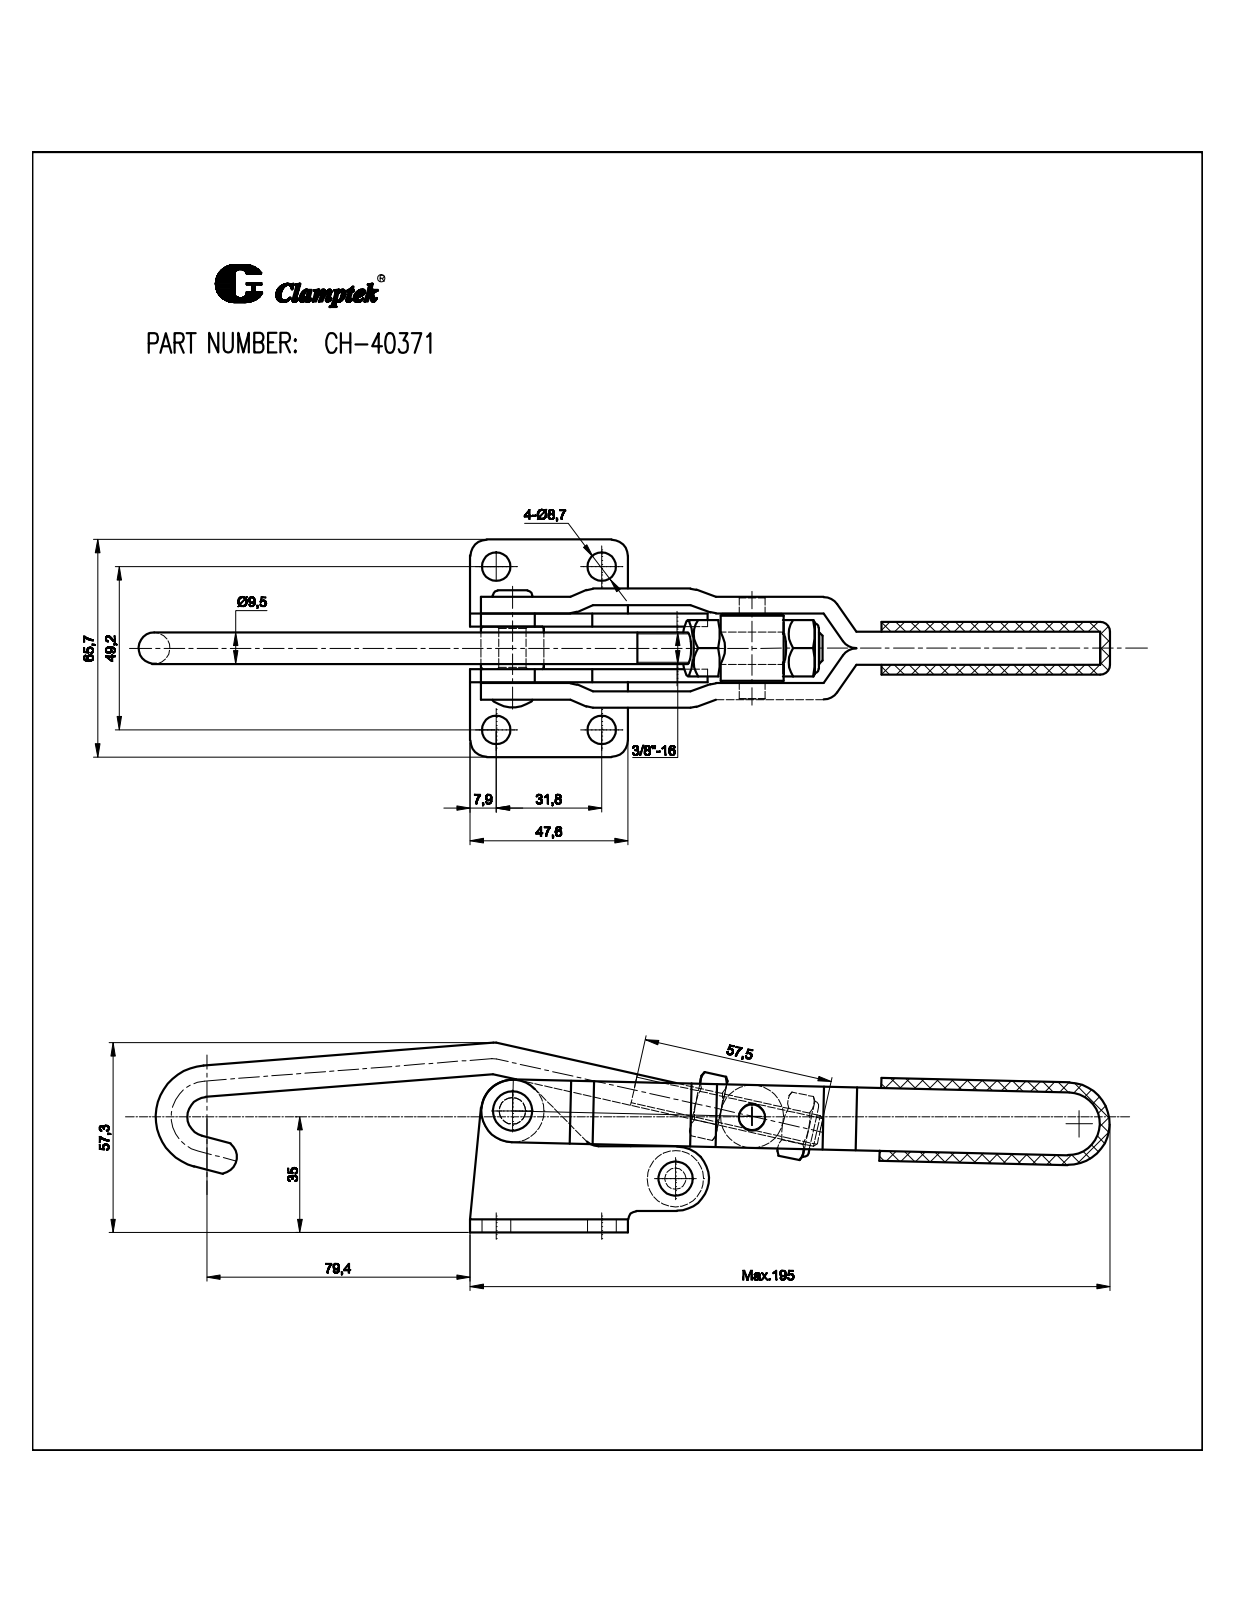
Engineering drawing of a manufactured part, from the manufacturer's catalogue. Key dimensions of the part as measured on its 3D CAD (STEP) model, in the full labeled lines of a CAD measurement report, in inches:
Part name (STEP PRODUCT): CH-40371
STEP written by: SolidWorks 2008 (CONFIG_CONTROL_DESIGN)
Units: inches
Bodies: 13 solids, 717 faces (243 planar, 235 cylindrical, 239 other)
Overall size (bounding box): 11.422 × 2.583 × 2.22
Volume: 5.747 in³ · Surface area: 92.11 in²
Round holes (diameter × count): ⌀0.343 ×4, ⌀0.335 ×3, ⌀0.315 ×2, ⌀0.06 ×1, ⌀0.181 ×1, ⌀0.236 ×1, ⌀0.252 ×1, ⌀0.256 ×1, ⌀0.386 ×1
Round bosses / shafts (diameter × count): ⌀0.374 ×3, ⌀0.748 ×2, ⌀0.551 ×1, ⌀0.472 ×1, ⌀0.054 ×1
Partial cylindrical surfaces — rounded edges, fillets, slot ends (radius × count): R0.197 ×17, R0.059 ×4, R0.157 ×2, R0.098 ×1, R0.374 ×1, R0.384 ×1, R0.433 ×1
Main face-to-face distances: 0.197, 0.409, 0.606, 0.157, 0.213, 0.449, 0.252, 0.508, 0.055, 0.661
Hole centre spacings: 1.252, 1.937, 2.306, 0.751, 1.215, 1.926, 2.093, 2.846
